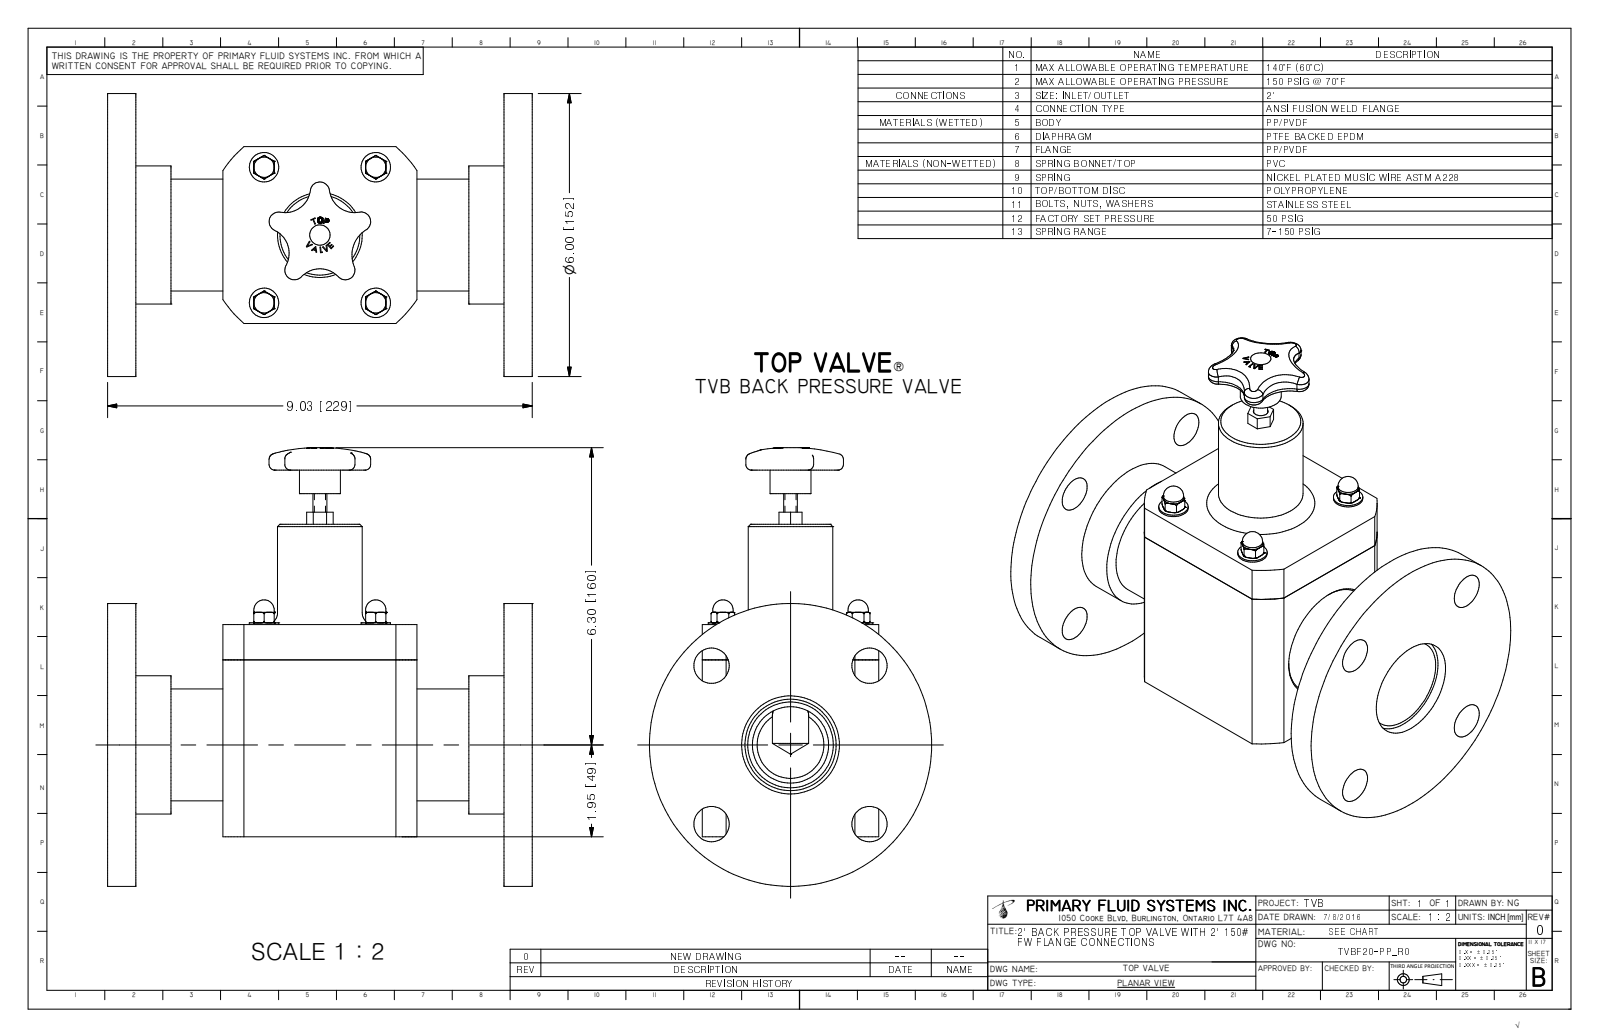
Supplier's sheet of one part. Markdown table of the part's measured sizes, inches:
| quantity | value |
| --- | --- |
| part name | TVBF20-PP_R0 |
| STEP written by | Autodesk Inventor 2009 (AUTOMOTIVE_DESIGN) |
| units | inches |
| bodies | 1 solid, 361 faces (152 planar, 61 cylindrical, 148 other) |
| overall size | 9.302 × 9.03 × 6 |
| volume | 107 in³ |
| surface area | 316.5 in² |
| round holes (diameter × count) | 0.175 × 4, 0.75 × 4, 1.939 × 1, 2.08 × 1 |
| round bosses / shafts (diameter × count) | 0.625 × 4, 0.433 × 4, 0.375 × 4, 6 × 1, 2.93 × 1, 2.375 × 1, 1.8 × 1, 0.87 × 1 |
| partial cylindrical surfaces (radius × count) | 0.085 × 5, 0.205 × 5, 0.536 × 4, 0.656 × 4, 0.625 × 1, 0.745 × 1, 2.475 × 1 |
| main face-to-face distances | 0.6, 8.43, 9.03, 7.83, 2.452, 6.578, 1.852, 5.978, 3.75, 4.5 |
| hole center spacings | 2.375, 3.359, 2.375, 2.875, 3.729, 4.75 |
